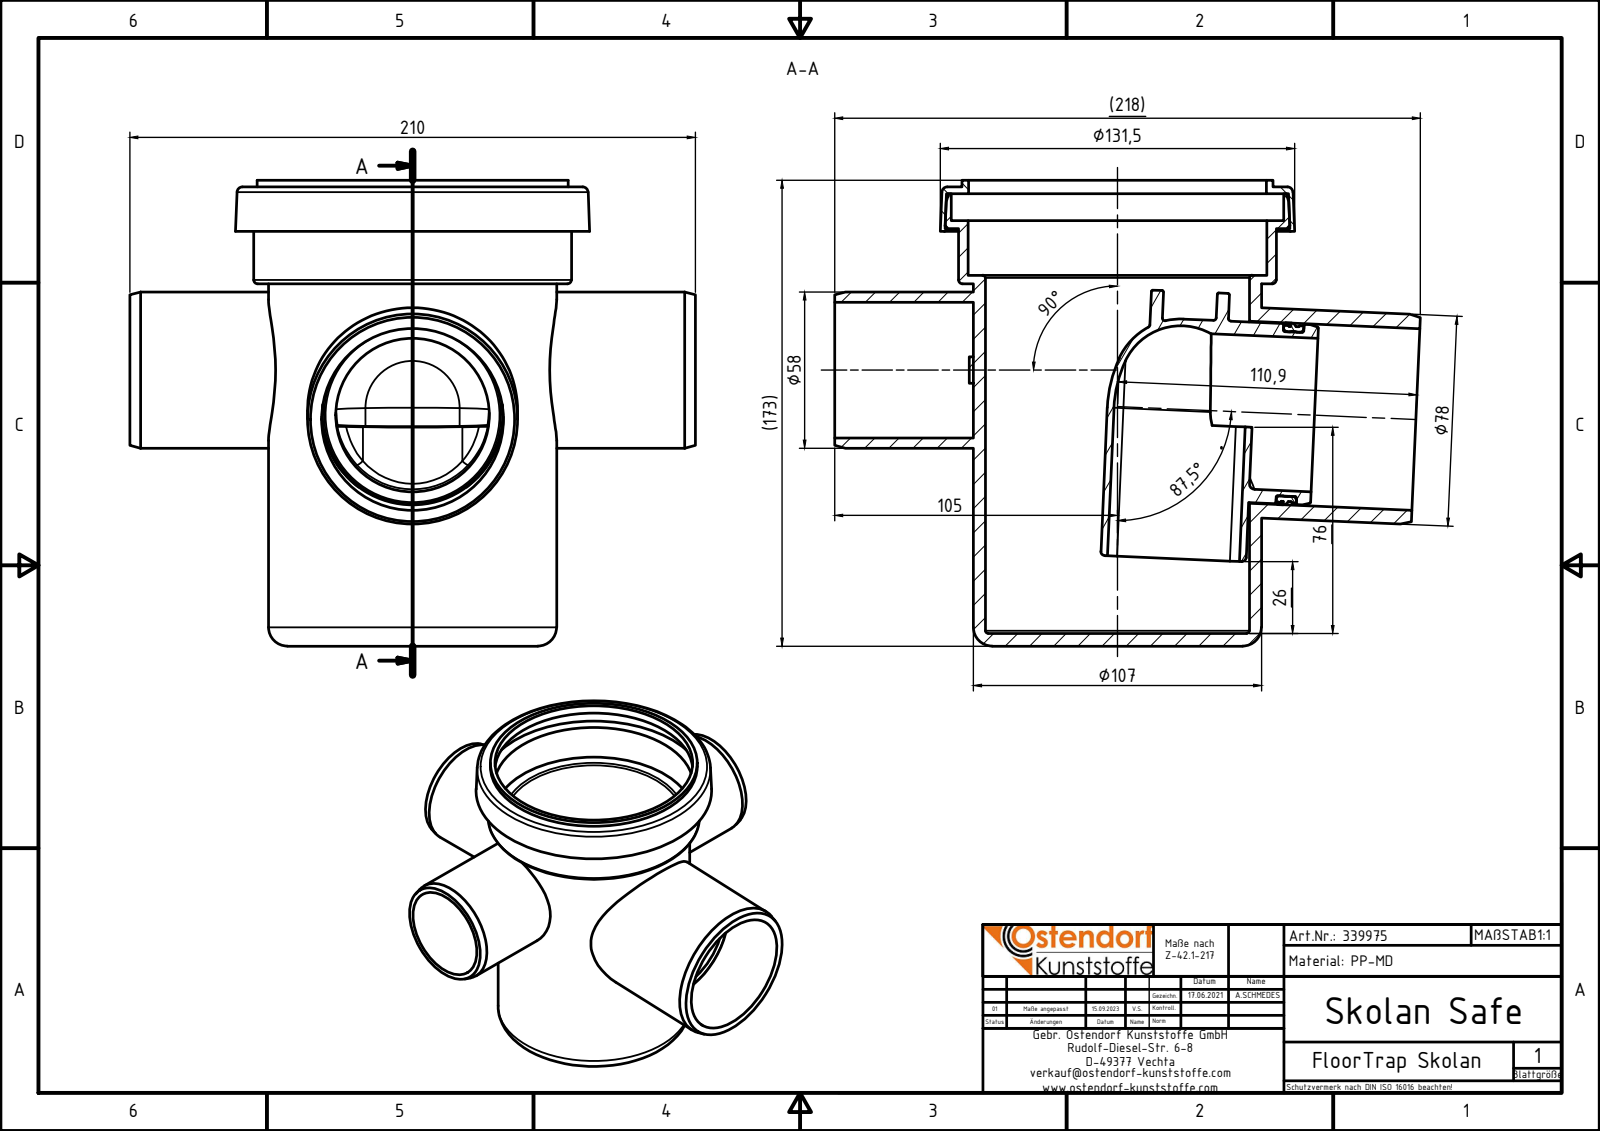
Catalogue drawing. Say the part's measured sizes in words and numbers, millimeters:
The part is named "339970 FloorTrap .idw; 339970 FloorTrap; 339970 FloorTrap Klickring; 339970 Floor Trap Einsatz". Its 3-D file was written by "Autodesk Inventor 2021 (AUTOMOTIVE_DESIGN)". It is 5 solids with 179 faces: 41 planar, 64 cylindrical and 74 other. Overall it measures 217.45 by 210 by 173 millimeters. Its volume is 540 047 cubic millimeters and its surface area 286 472 square millimeters. Round holes: 2 of diameter 50.4, 1 of diameter 57, 1 of diameter 61, 1 of diameter 65.8, 1 of diameter 67.5, 1 of diameter 98, 1 of diameter 110.5, 1 of diameter 110.9, 1 of diameter 123.5, 1 of diameter 126.5. Round bosses or shafts: 2 of diameter 58, 2 of diameter 9.8, 1 of diameter 125.6, 1 of diameter 118, 1 of diameter 115.5, 1 of diameter 107, 1 of diameter 78, 1 of diameter 67.5. Partial cylindrical surfaces (rounded edges, fillets, slot ends): 8 of radius 0.5, 4 of radius 5, 2 of radius 1, 2 of radius 22.75, 2 of radius 25.25, 2 of radius 43.75, 2 of radius 45.5, 2 of radius 48. The main face-to-face distances are 4.7, 168, 163.3, 2.5, 158, 153.3, 10, 170.5, 165.8, 12.5.
